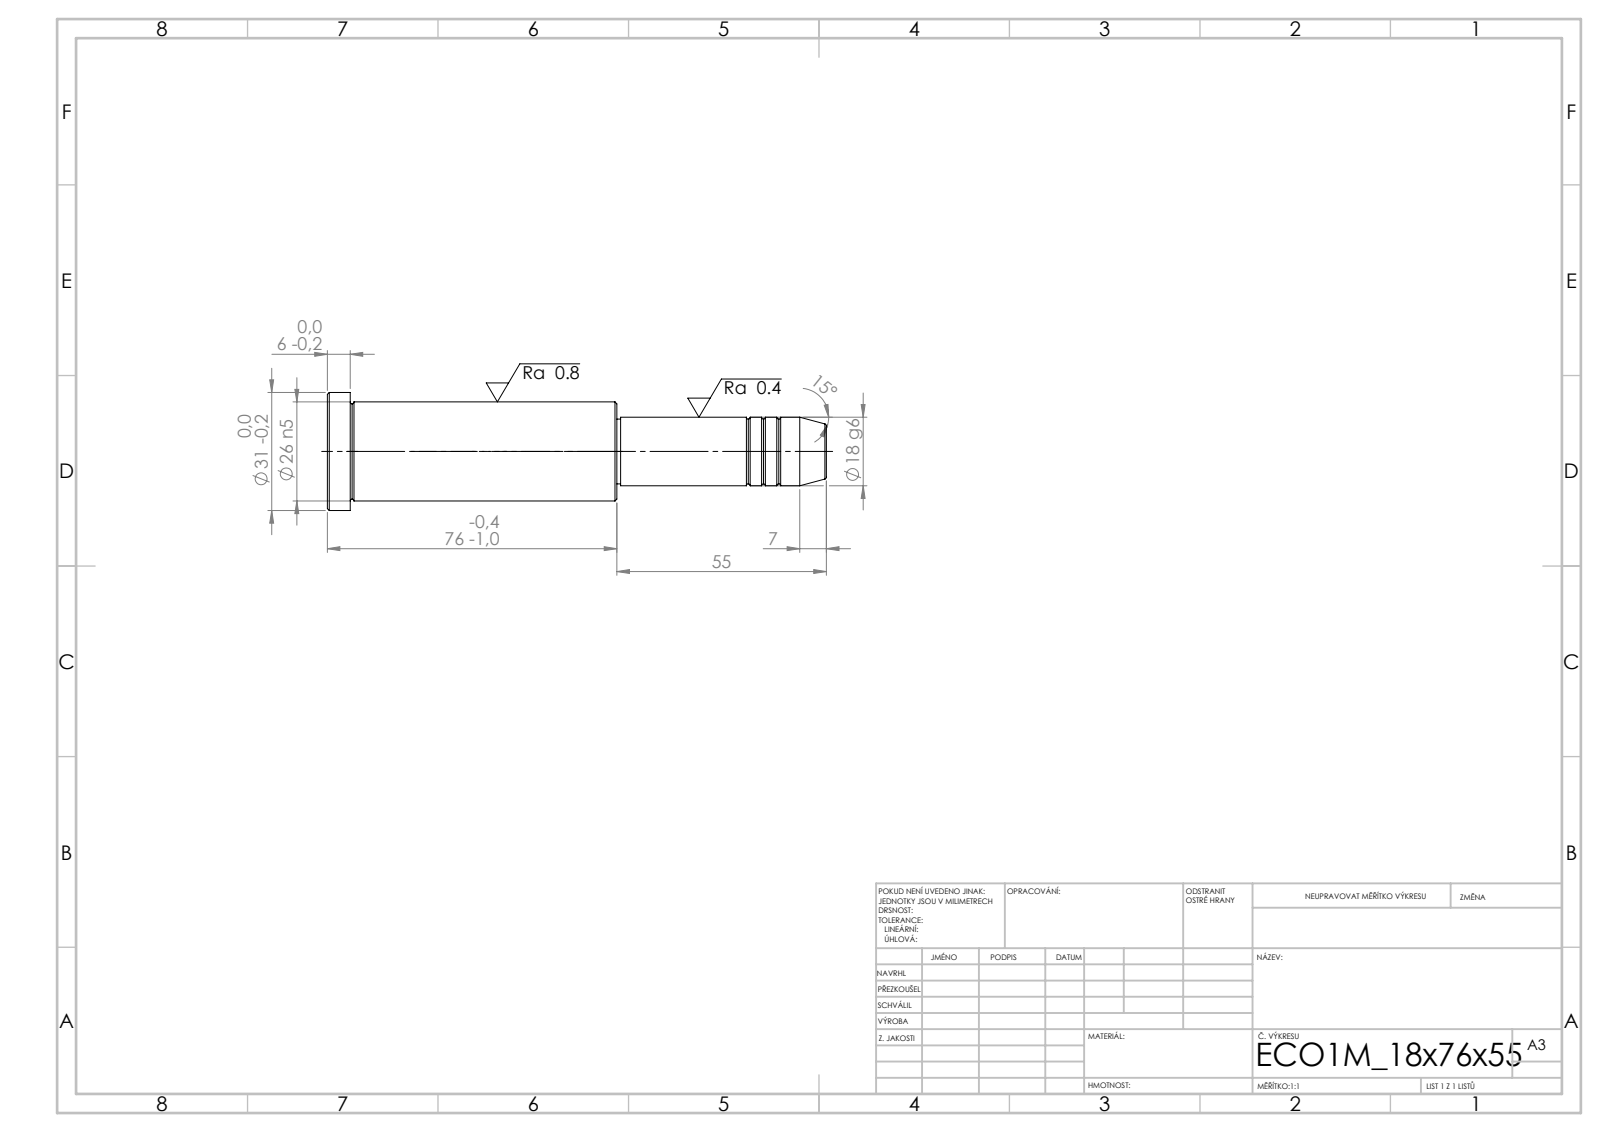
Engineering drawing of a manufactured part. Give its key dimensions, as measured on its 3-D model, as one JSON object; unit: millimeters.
{"step_written_by": "SolidWorks 2019 (CONFIG_CONTROL_DESIGN)", "units": "millimeters", "bodies": {"solids": 1, "faces": 43, "planar": 5, "cylindrical": 14, "other": 24}, "overall_size": [131, 31, 31], "volume_mm3": 55197, "surface_area_mm2": 10922, "round_bosses_or_shafts": [[31, 1], [26, 1], [18, 1], [17, 1]], "face_to_face_distances": [76, 70, 6, 55, 125, 131, 54, 1, 71, 77]}
